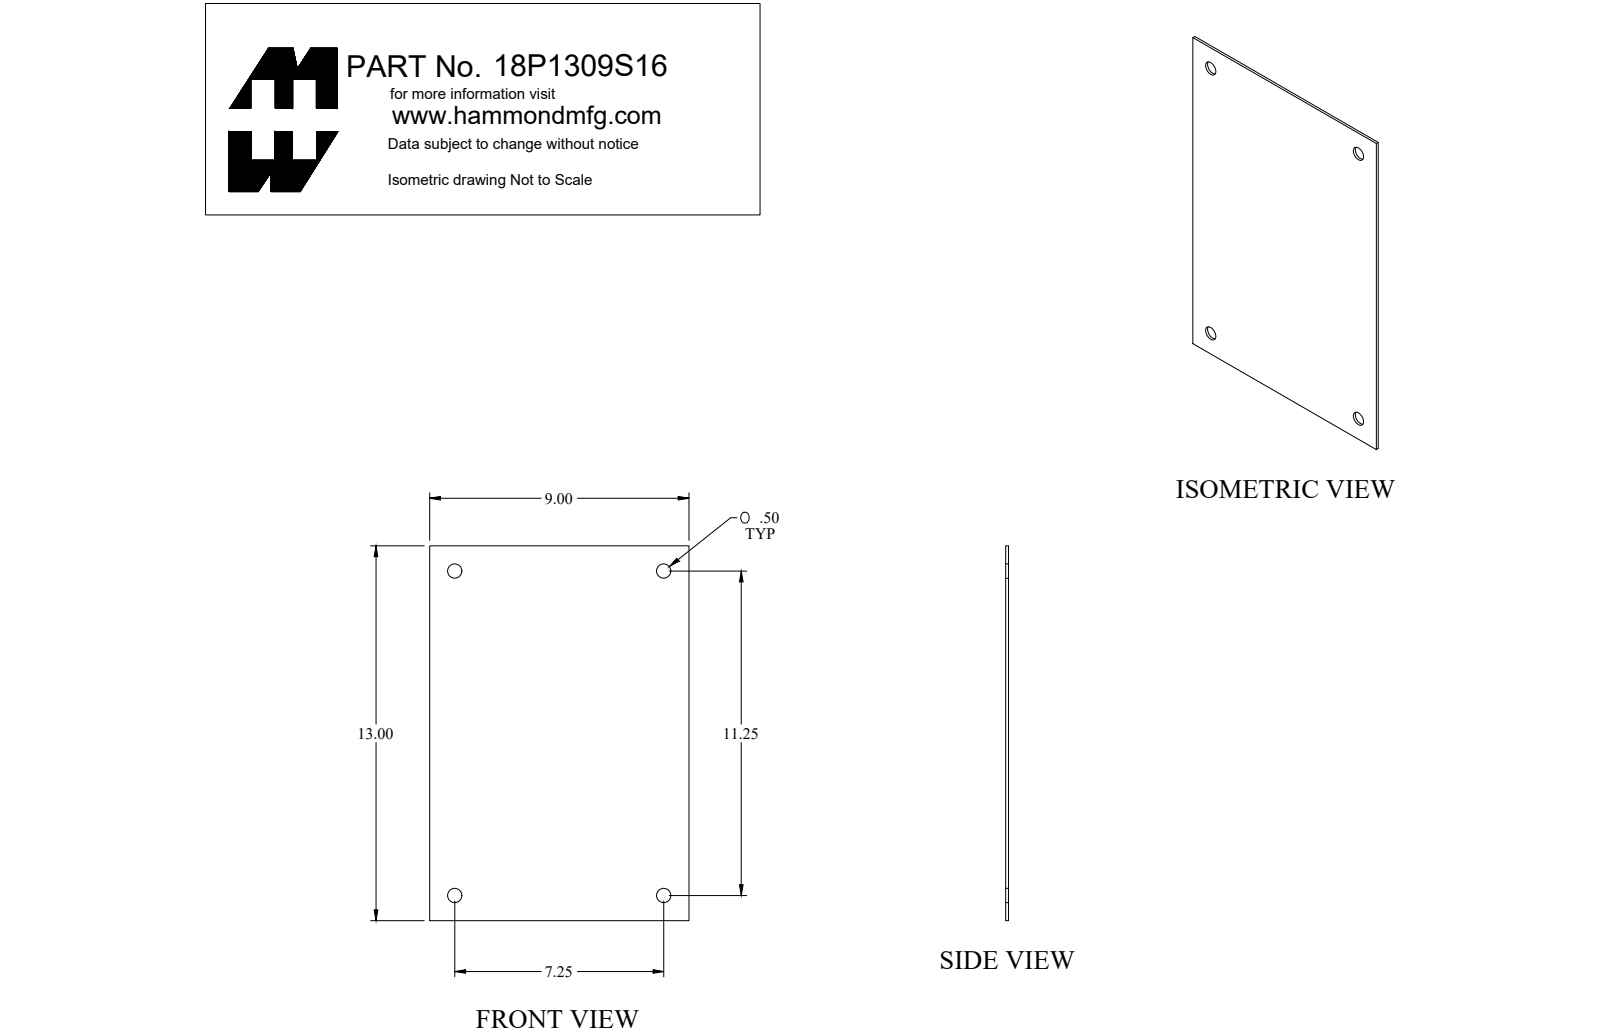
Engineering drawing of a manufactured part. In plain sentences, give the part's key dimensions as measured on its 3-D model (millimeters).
The part is named "18P1309S16_Default". Its 3-D file was written by "SolidWorks 2018 (CONFIG_CONTROL_DESIGN)". It is 1 solid with 14 faces: 6 planar, 8 cylindrical and 0 other. Overall it measures 330.2 by 228.6 by 2.4 millimeters. Its volume is 180 900 cubic millimeters and its surface area 153 000 square millimeters. Round holes: 4 of diameter 12.7. The main face-to-face distances are 2.4, 228.6, 330.2. The hole center spacings are 184.2, 285.8, 340.
